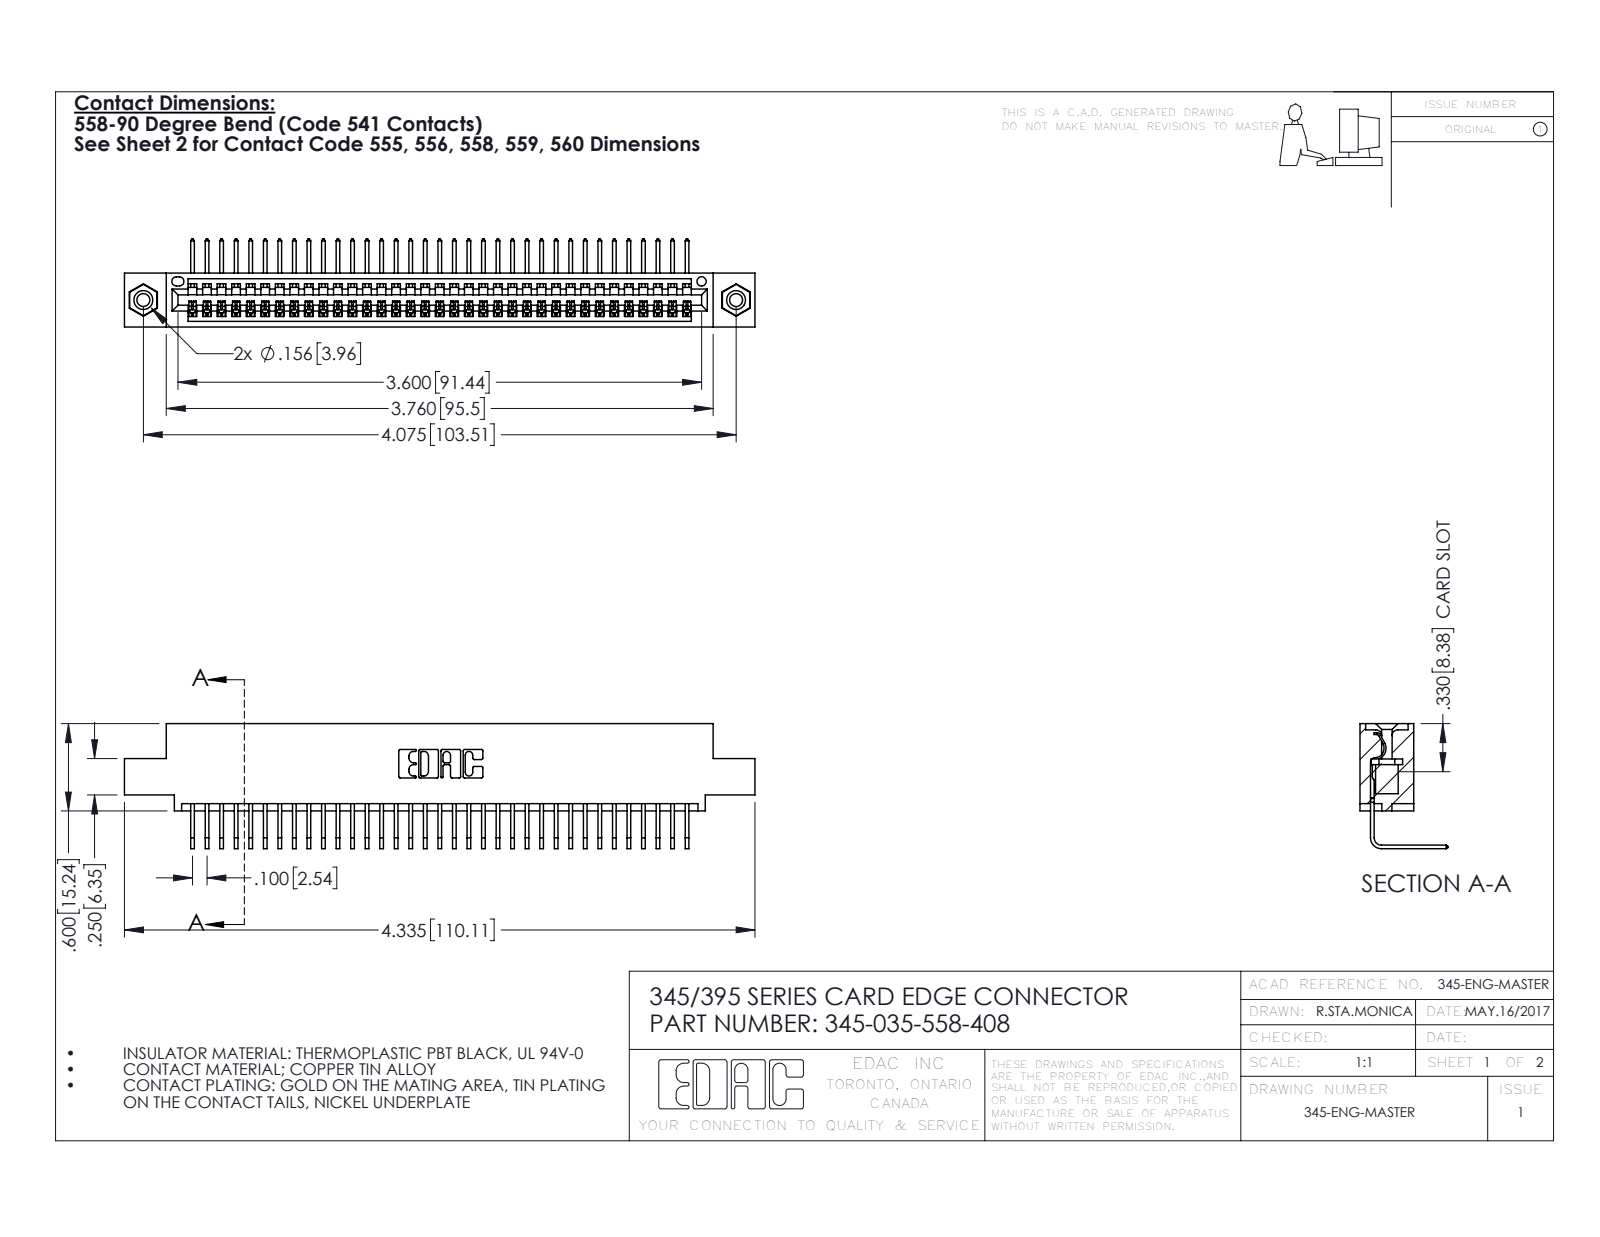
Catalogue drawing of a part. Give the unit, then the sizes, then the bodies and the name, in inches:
Units: inches
Overall size (bounding box): 4.335 × 0.859 × 0.605
Round holes (diameter × count): ⌀0.089 ×2, ⌀0.125 ×2, ⌀0.156 ×2, ⌀0.064 ×1
Round bosses / shafts (diameter × count): ⌀0.155 ×2
Partial cylindrical surfaces — rounded edges, fillets, slot ends (radius × count): R0.006 ×70, R0.01 ×22, R0.007 ×6, R0.031 ×6, R0.026 ×3, R0.031 ×2, R0.04 ×2, R0.014 ×1
Main face-to-face distances: 0.072, 0.298, 0.37, 0.2, 0.098, 0.272, 0.025, 0.225, 0.149, 0.072
Hole centre spacings: 0.27, 3.839, 4.075
Volume: 0.637 in³ · Surface area: 22.57 in²
Bodies: 38 solids, 2290 faces (1586 planar, 688 cylindrical, 16 other)
Part name (STEP PRODUCT): 345-292-001_558 Tail - 2; 345-035-558-408; 345-250-001_345-250-003-102; 345 Part_0.110 Offset - 0.156 Dia-TI
STEP written by: SolidWorks 2016 (CONFIG_CONTROL_DESIGN)
